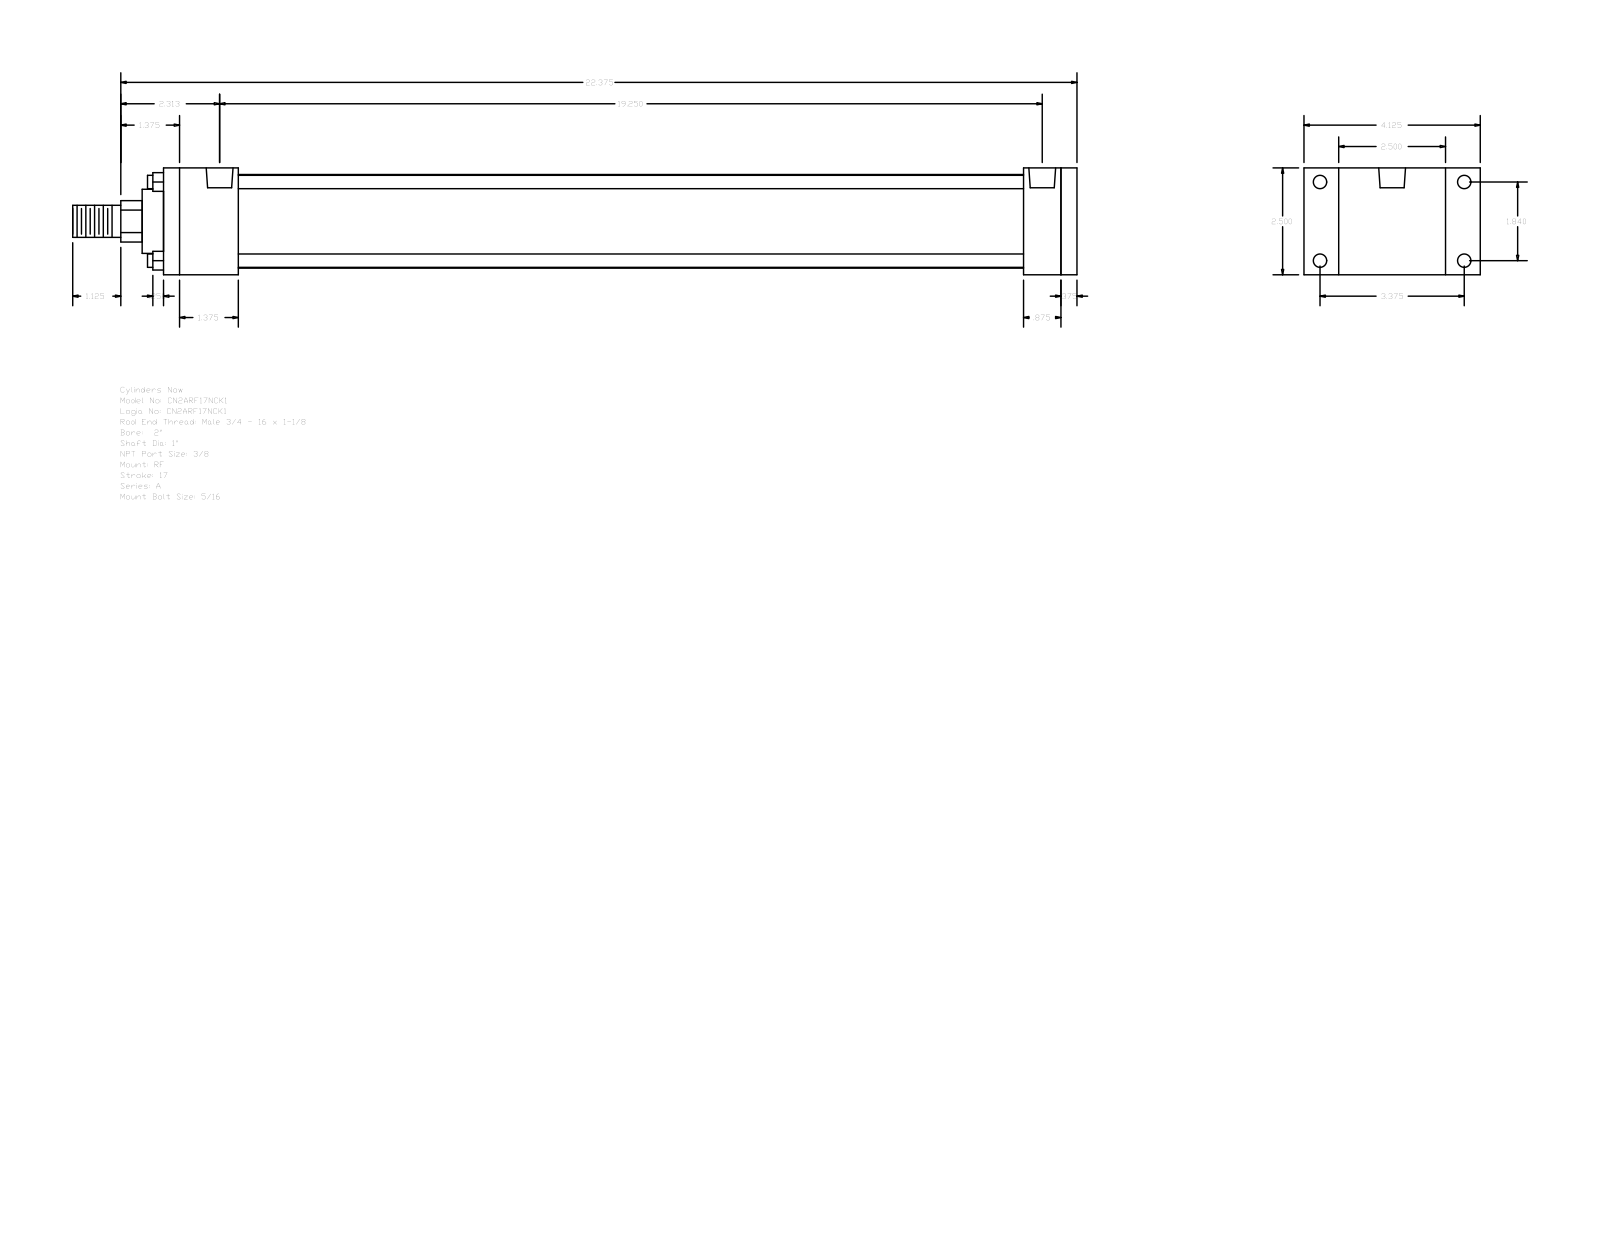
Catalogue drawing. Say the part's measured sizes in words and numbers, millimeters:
The part is named "A_RF__0200_1". Its 3-D file was written by "GSSL Pune (CONFIG_CONTROL_DESIGN)". It is 0 solids with 92 faces: 64 planar, 28 cylindrical and 0 other. Overall it measures 596.9 by 104.78 by 63.5 millimeters. Round holes: 4 of diameter 5.56, 4 of diameter 7.94, 2 of diameter 15.93. Round bosses or shafts: 4 of diameter 7.94, 1 of diameter 55.63, 1 of diameter 38.1, 1 of diameter 25.4, 1 of diameter 19.05. Partial cylindrical surfaces (rounded edges, fillets, slot ends): 1 of radius 12.29. The main face-to-face distances are 63.5, 9.53, 542.93, 533.4, 44.45, 20.64, 488.95, 498.48, 511.18, 466.73. The hole center spacings are 46.74, 85.72, 97.63, 483.38, 1.59, 3.98, 484.97, 487.36.
